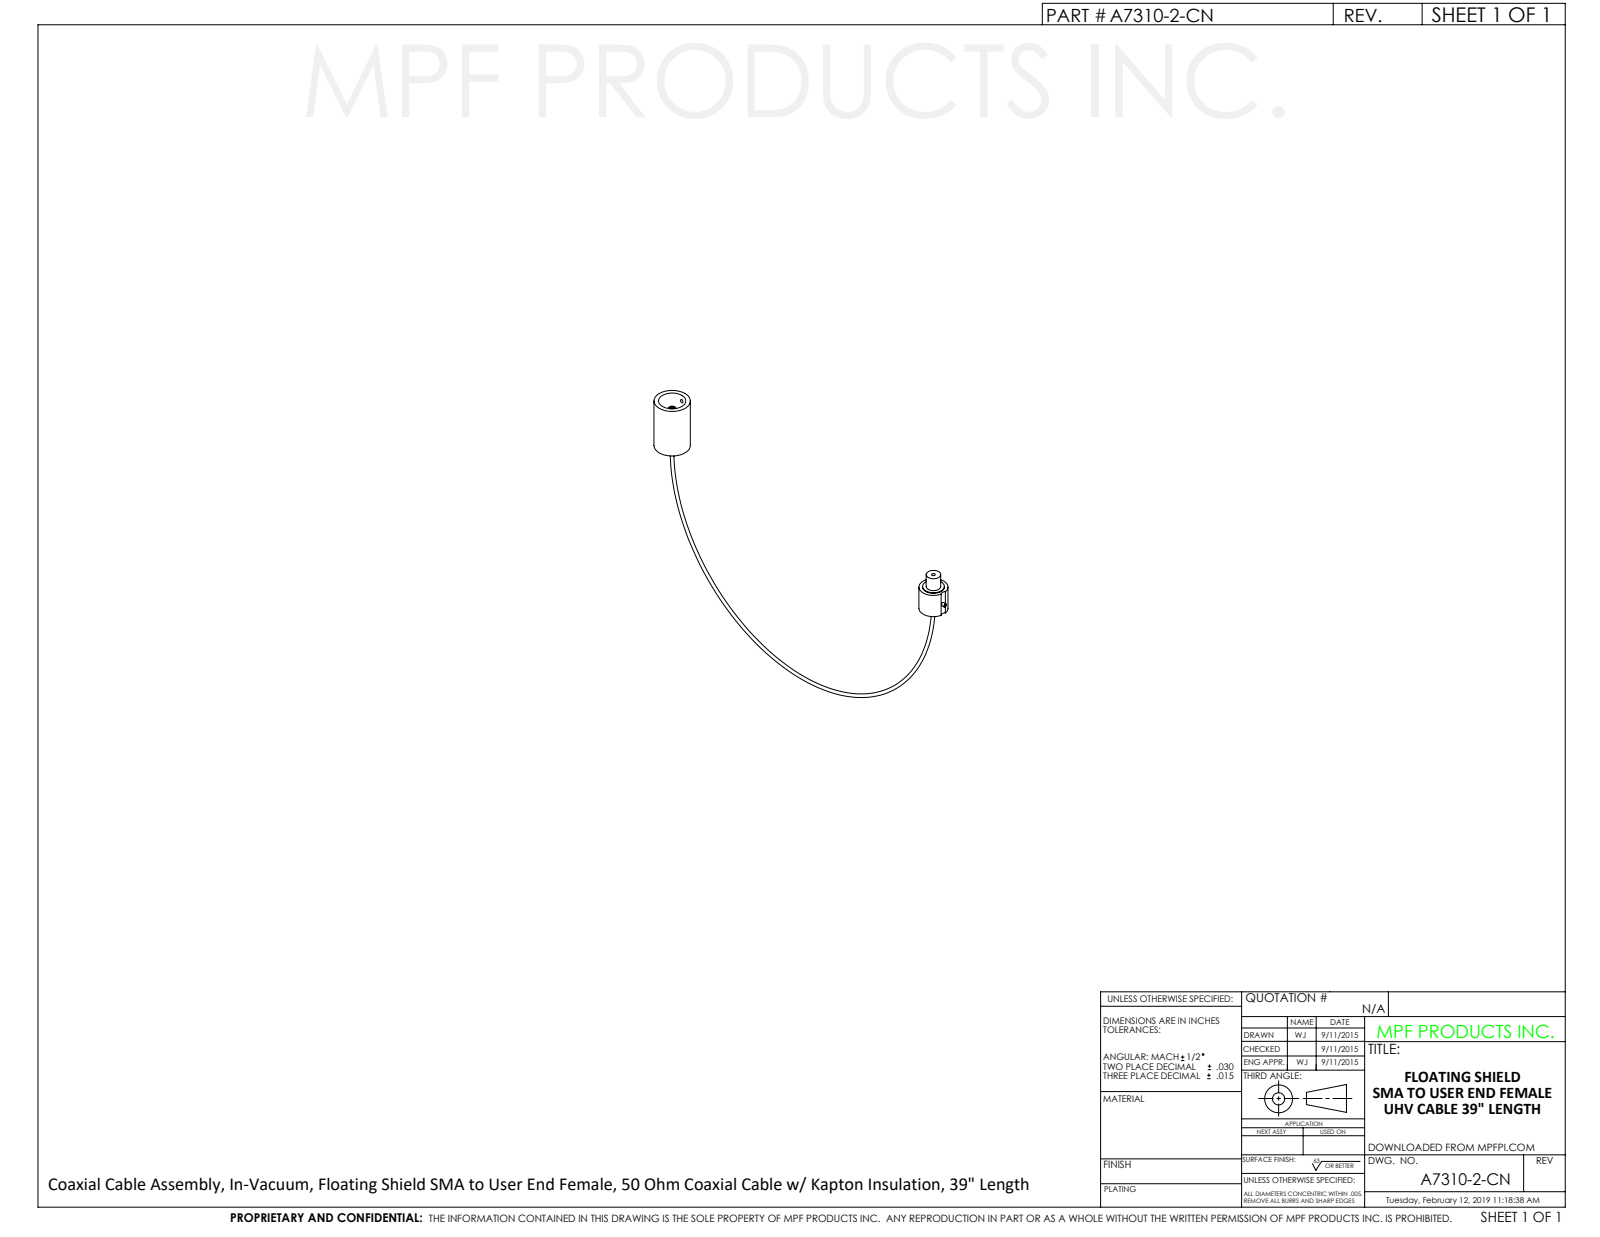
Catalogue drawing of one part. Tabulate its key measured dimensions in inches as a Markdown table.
| quantity | value |
| --- | --- |
| part name | A7309-2-CN |
| STEP written by | SolidWorks 2012 (CONFIG_CONTROL_DESIGN) |
| units | inches |
| bodies | 1 solid, 71 faces (30 planar, 36 cylindrical, 5 other) |
| overall size | 11.118 × 6.833 × 1 |
| volume | 1.403 in³ |
| surface area | 17.11 in² |
| round holes (diameter × count) | 0.1 × 4, 0.025 × 1, 0.2 × 1, 0.75 × 1 |
| round bosses / shafts (diameter × count) | 1 × 1, 0.8 × 1, 0.6 × 1, 0.4 × 1, 0.2 × 1, 0.11 × 1, 0.101 × 1 |
| partial cylindrical surfaces (radius × count) | 0.138 × 1 |
| main face-to-face distances | 0.398, 1.898, 1.5, 0.714, 0.315, 1.185, 0.02, 0.734, 0.335, 1.165 |
| hole center spacings | 0.35, 0.578, 10.162 |
